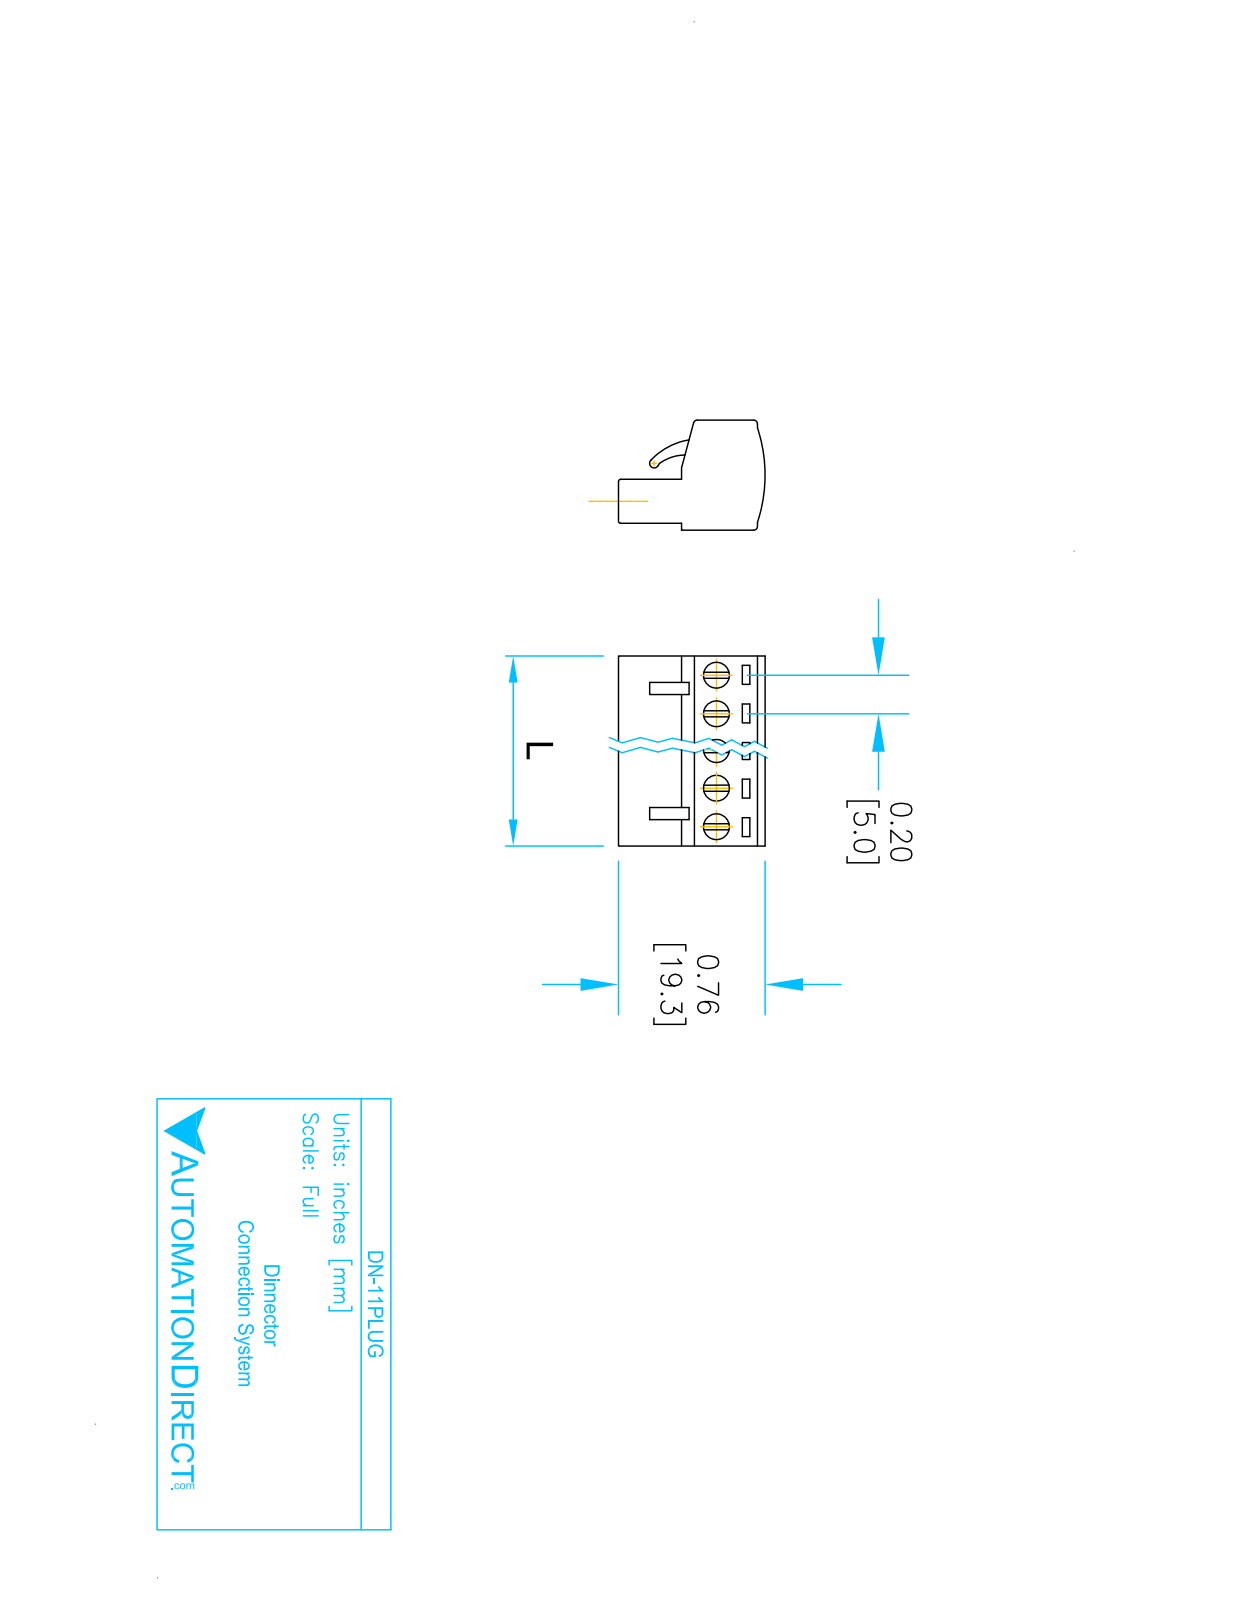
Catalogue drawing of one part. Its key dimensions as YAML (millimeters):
part_name: "49011_S; 49002_S; 49001_S; 49001_S_49002_SENZA DENTE"
step_written_by: "SolidWorks 2013 (AUTOMOTIVE_DESIGN)"
units: millimeters
bodies: {solids: 10, faces: 1007, planar: 709, cylindrical: 243, other: 55}
overall_size: [55.88, 19.3, 14.5]
volume: 9545
surface_area: 9935
round_holes:
  - {diameter: 1.6, count: 11}
  - {diameter: 2.5, count: 11}
  - {diameter: 3.4, count: 11}
  - {diameter: 3.6, count: 11}
round_bosses_or_shafts:
  - {diameter: 3, count: 11}
partial_cylinders:
  - {radius: 2.9, count: 11}
  - {radius: 0.5, count: 3}
  - {radius: 0.3, count: 2}
  - {radius: 0.6, count: 1}
  - {radius: 6, count: 1}
  - {radius: 9, count: 1}
  - {radius: 20.03, count: 1}
face_to_face_distances: [5.08, 10.16, 15.24, 20.32, 25.4, 30.48, 35.56, 40.64, 6.7, 1]
hole_center_spacings: [5.08, 10.16, 15.24, 20.32, 25.4, 30.48, 35.56, 40.64]
